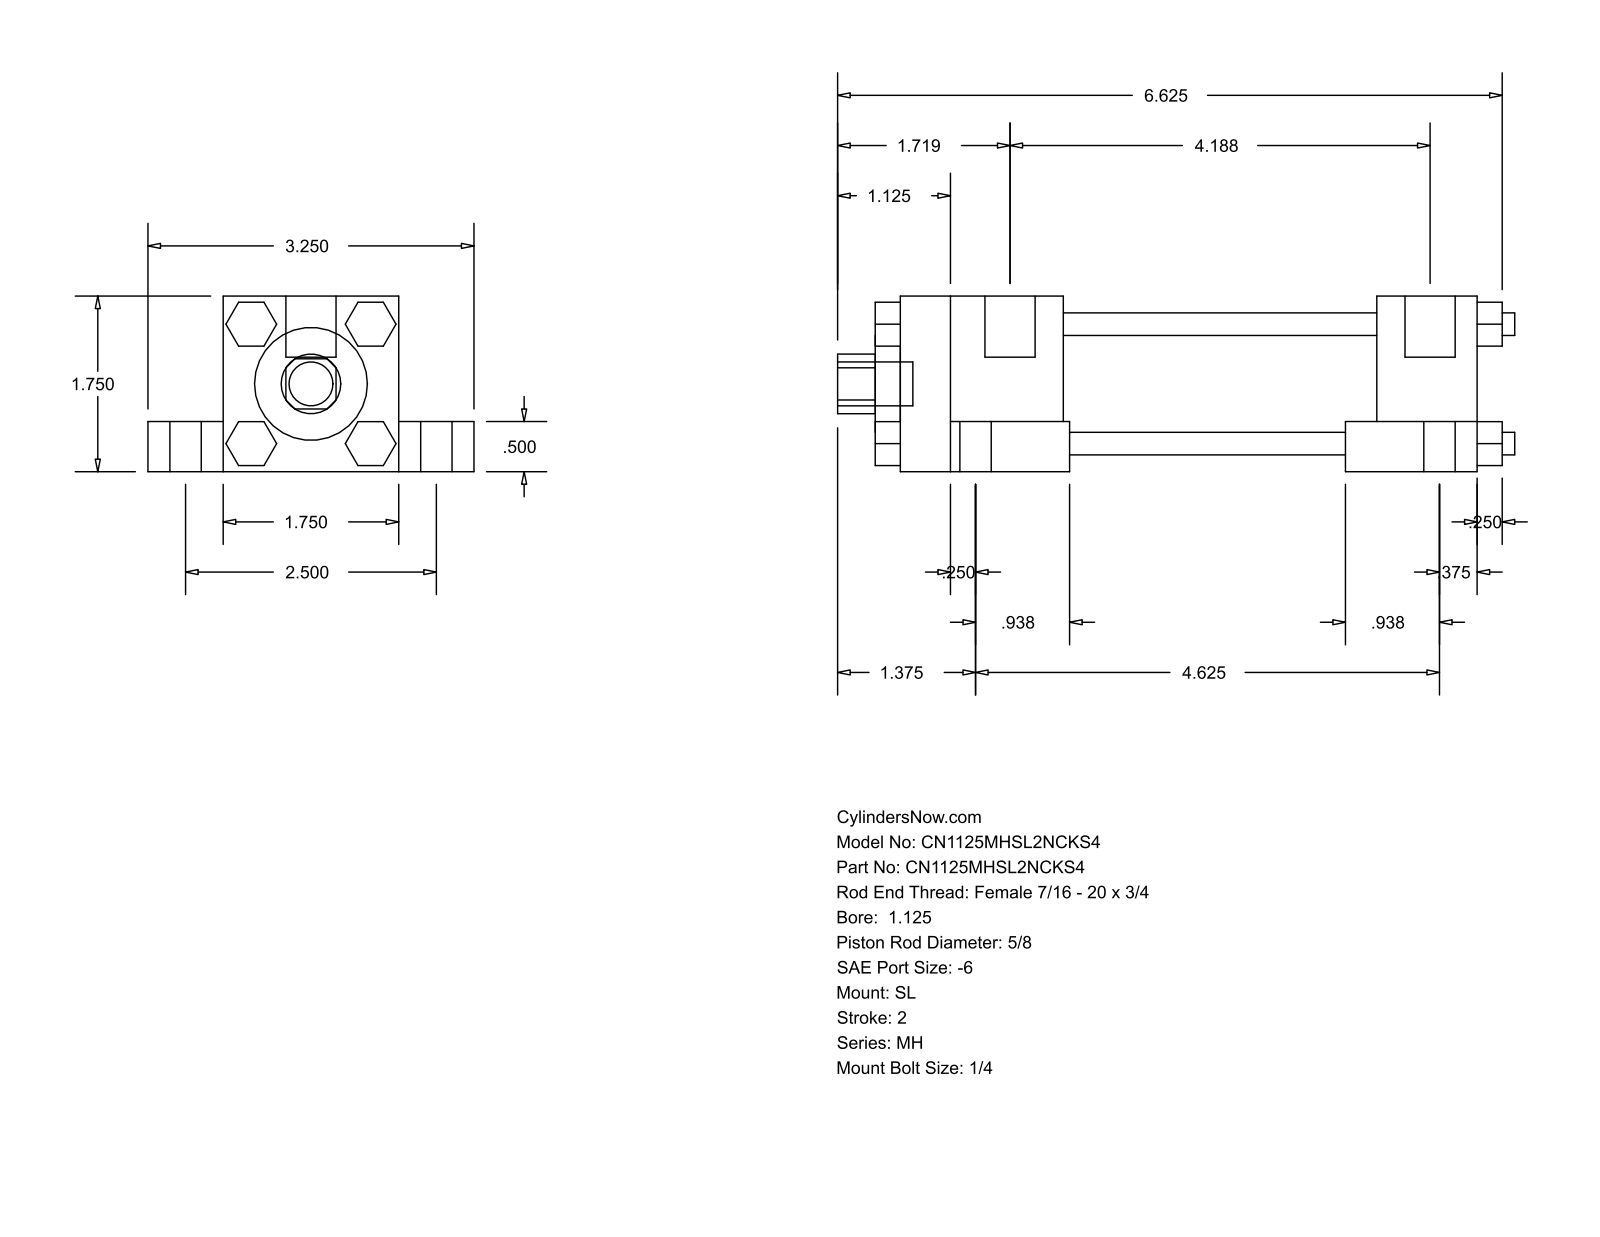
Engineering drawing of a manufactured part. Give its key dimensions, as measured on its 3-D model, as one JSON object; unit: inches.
{"part_name": "MH_SL__0112_0.625", "step_written_by": "GSSL Pune (CONFIG_CONTROL_DESIGN)", "units": "inches", "bodies": {"solids": 0, "faces": 150, "planar": 114, "cylindrical": 36, "other": 0}, "overall_size": [6.75, 3.25, 1.75], "round_holes": [[0.625, 1], [1.125, 1], [1.375, 1]], "round_bosses_or_shafts": [[0.563, 4], [0.313, 4], [0.225, 4], [0.219, 4], [0.5, 2], [0.437, 1]], "partial_cylinders_radius": [[0.297, 1]], "face_to_face_distances": [1.75, 0.75, 0.5, 1.25, 2.5, 0.25, 6, 0.437, 1.313, 3.938]}
